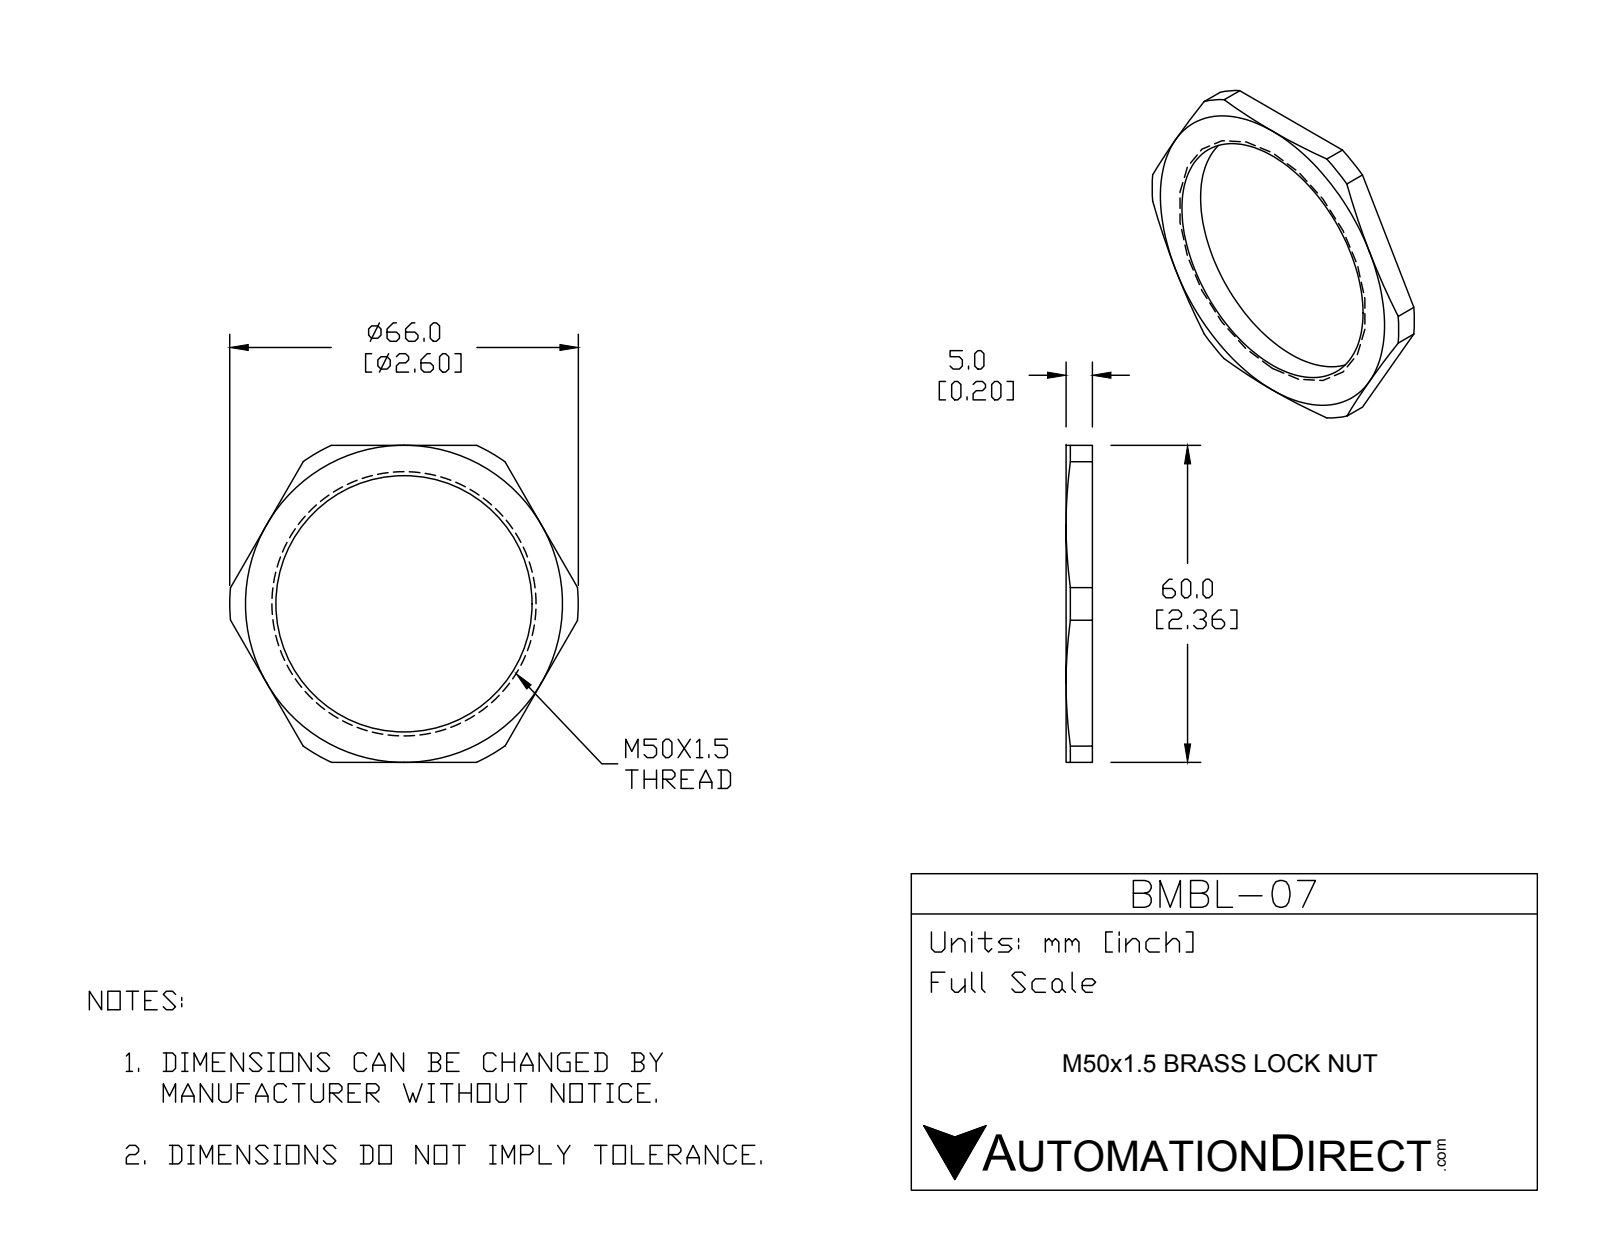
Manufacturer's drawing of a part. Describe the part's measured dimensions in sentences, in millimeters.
The part is named "BMBL-07". Its 3-D file was written by "SolidWorks 2015 (CONFIG_CONTROL_DESIGN)". It is 1 solid with 23 faces: 8 planar, 9 cylindrical and 6 other. Overall it measures 66 by 60 by 5 millimeters. Its volume is 6 122 cubic millimeters and its surface area 4 188 square millimeters. Round holes: 1 of diameter 48.5. Partial cylindrical surfaces (rounded edges, fillets, slot ends): 1 of radius 33. The main face-to-face distances are 5, 60.
